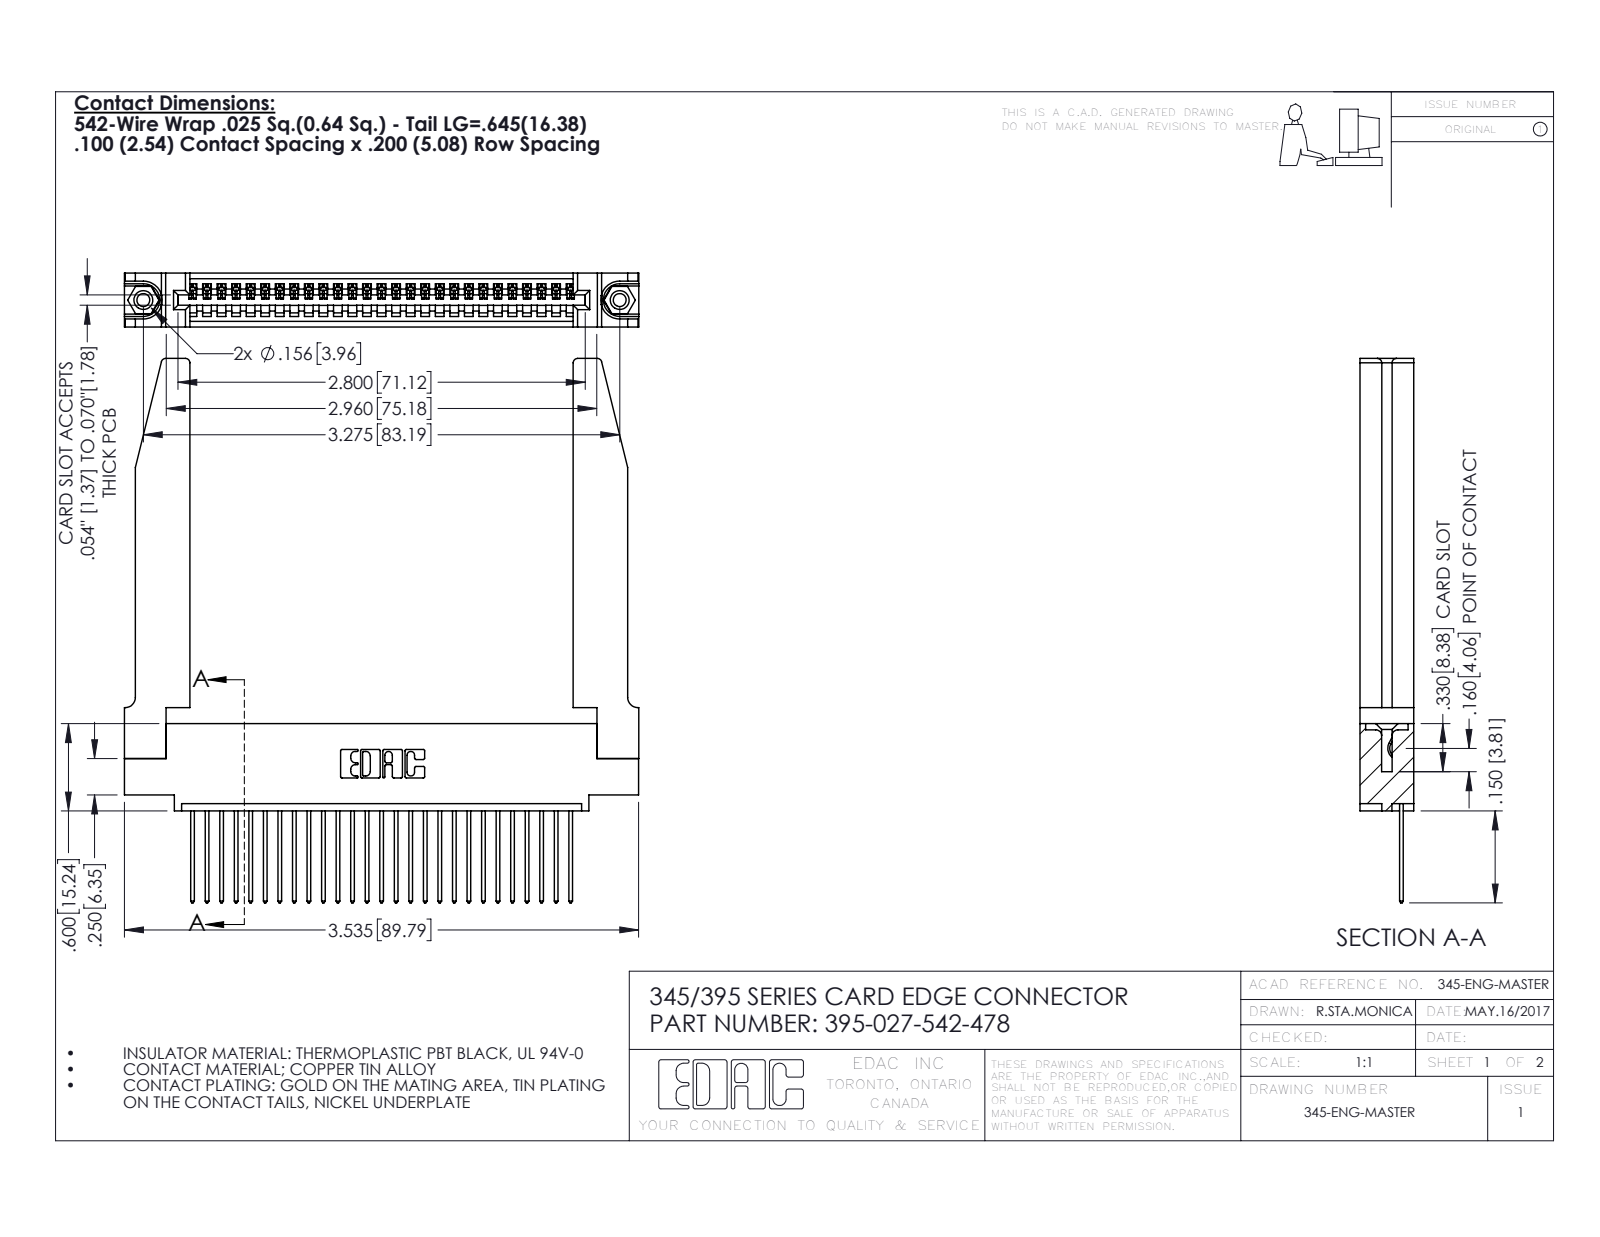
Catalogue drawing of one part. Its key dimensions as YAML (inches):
part_name: "395-027-542-478; 345-292-001_345-293-142; 345-220-078_345-220-078; 345 Part_0.110 Offset - 0.156 Dia-TH (+1 more)"
step_written_by: "SolidWorks 2016 (CONFIG_CONTROL_DESIGN)"
units: inches
bodies: {solids: 32, faces: 1930, planar: 1306, cylindrical: 572, other: 52}
overall_size: [3.742, 3.536, 0.37]
volume: 0.986
surface_area: 28.3
round_holes:
  - {diameter: 0.089, count: 2}
  - {diameter: 0.125, count: 2}
  - {diameter: 0.156, count: 2}
  - {diameter: 0.064, count: 1}
round_bosses_or_shafts:
  - {diameter: 0.155, count: 2}
partial_cylinders:
  - {radius: 0.006, count: 54}
  - {radius: 0.01, count: 54}
  - {radius: 0.01, count: 22}
  - {radius: 0.03, count: 8}
  - {radius: 0.007, count: 6}
  - {radius: 0.031, count: 6}
  - {radius: 0.026, count: 3}
  - {radius: 0.031, count: 2}
face_to_face_distances: [0.37, 0.072, 0.298, 0.098, 0.272, 0.025, 0.2, 0.148, 0.15, 0.225]
hole_center_spacings: [0.27, 3.04, 3.275]
